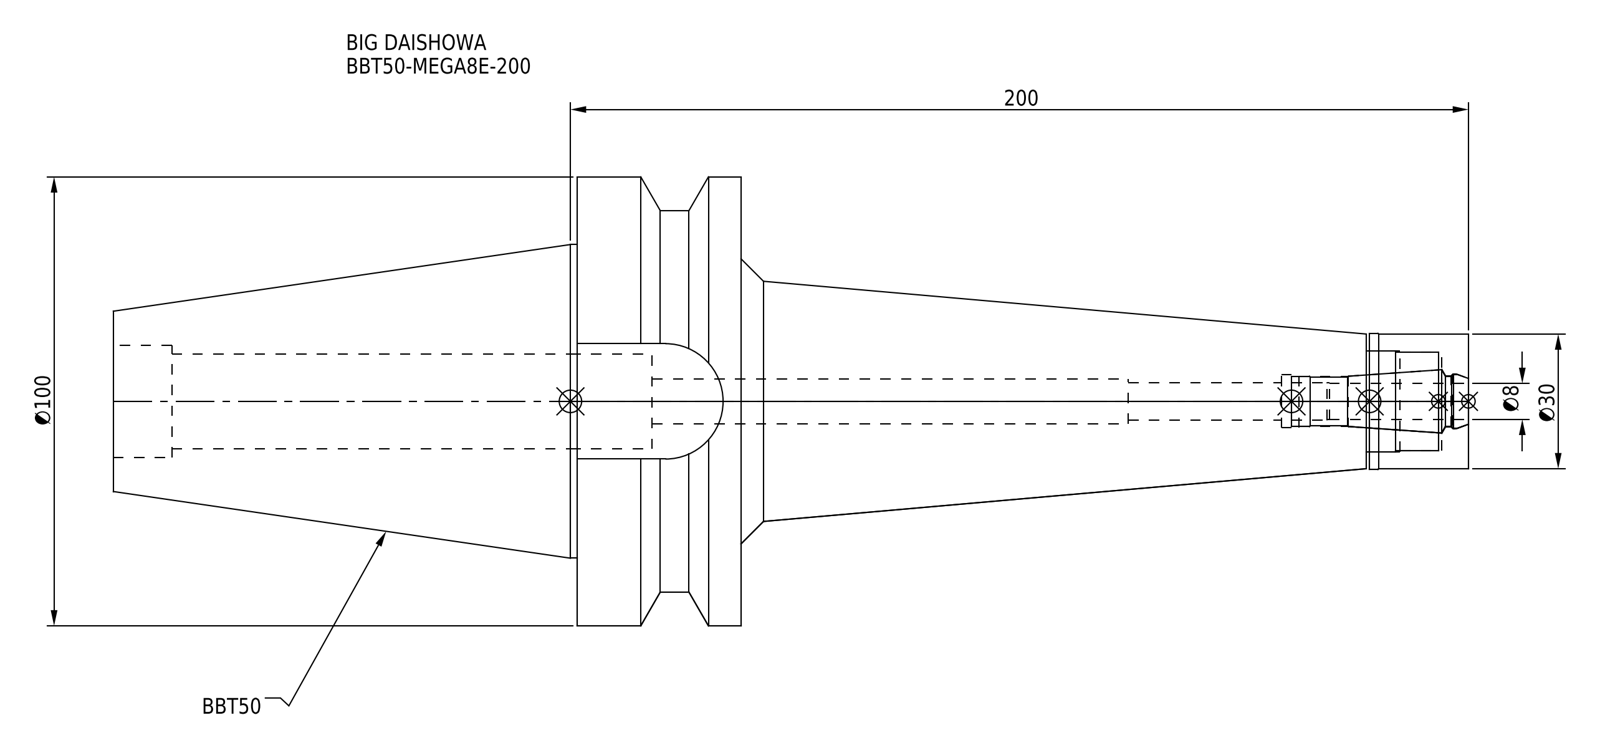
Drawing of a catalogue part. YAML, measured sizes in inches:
part_name: "DXF_TEMP_ASSY_ASM_4_ASM.stp; MEN8_1.stp; BBT50-MEGA8E-200_1.stp; BBT50-MEGA8E-200-080-FreeParts (+3 more)"
step_written_by: "SolidWorks 2019 (CONFIG_CONTROL_DESIGN)"
units: inches
bodies: {solids: 2, faces: 81, planar: 21, cylindrical: 40, other: 20}
overall_size: [11.882, 3.937, 3.937]
volume: 40.12
surface_area: 125.9
round_holes:
  - {diameter: 0.331, count: 1}
  - {diameter: 0.394, count: 1}
  - {diameter: 0.441, count: 1}
  - {diameter: 0.449, count: 1}
  - {diameter: 0.465, count: 1}
  - {diameter: 0.484, count: 1}
  - {diameter: 0.835, count: 1}
  - {diameter: 0.866, count: 1}
  - {diameter: 0.886, count: 1}
  - {diameter: 0.984, count: 1}
round_bosses_or_shafts:
  - {diameter: 3.937, count: 1}
  - {diameter: 3.346, count: 1}
  - {diameter: 2.75, count: 1}
  - {diameter: 1.193, count: 1}
  - {diameter: 1.181, count: 1}
partial_cylinders:
  - {radius: 0.506, count: 1}
face_to_face_distances: [1.437, 5.504, 4.067, 2.787, 6.378, 7.815, 11.882, 1.012, 0.866, 5.512]
